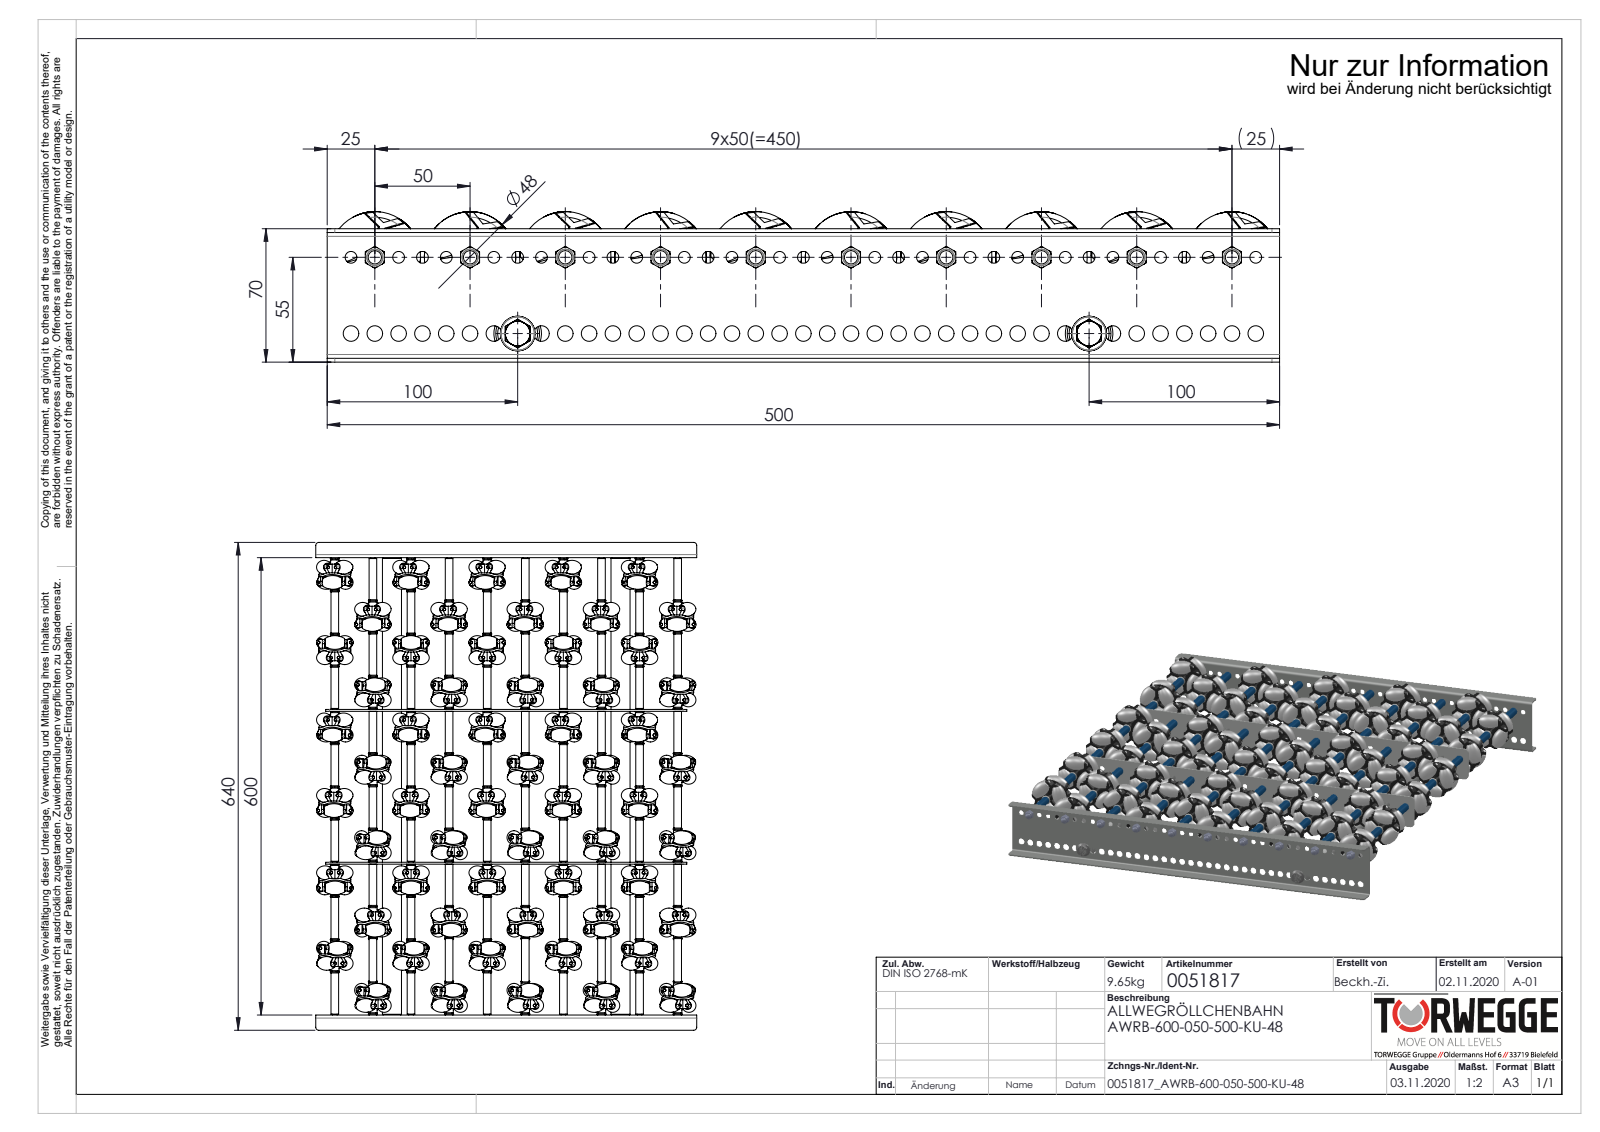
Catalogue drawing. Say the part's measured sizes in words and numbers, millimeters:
The part is named "S100994_Sperrzahnschraube_M08x16-8.8-A2K; 0051817; 0015028_AWR48; Profil-RB-20x70x20x2_S100208_U-PROFIL-20-70-20-2-RB-L=500 (+8 more)". Its 3-D file was written by "SolidWorks 2020 (AUTOMOTIVE_DESIGN)". It is 1004 solids with 17668 faces: 6192 planar, 6792 cylindrical and 4684 other. Overall it measures 640 by 500 by 79 millimeters. Its volume is 3 368 000 cubic millimeters and its surface area 2 286 000 square millimeters. Round holes: 360 of diameter 3.7, 360 of diameter 4.2, 39 of diameter 6.2, 39 of diameter 8.2, 19 of diameter 6.5, 10 of diameter 4.92, 10 of diameter 8.4, 2 of diameter 6.8, 2 of diameter 21. Round bosses or shafts: 360 of diameter 4, 291 of diameter 3.7, 12 of diameter 8, 10 of diameter 47.1, 10 of diameter 42, 10 of diameter 11, 10 of diameter 10, 10 of diameter 7. Partial cylindrical surfaces (rounded edges, fillets, slot ends): 8 of radius 4, 4 of radius 2, 4 of radius 5. The main face-to-face distances are 2, 602, 200.5, 2.5, 68, 3, 600, 604, 202.4, 201.1. The hole center spacings are 36.06, 36.05, 36.04, 36.07, 12.5, 87.5, 94.04, 75.9.
